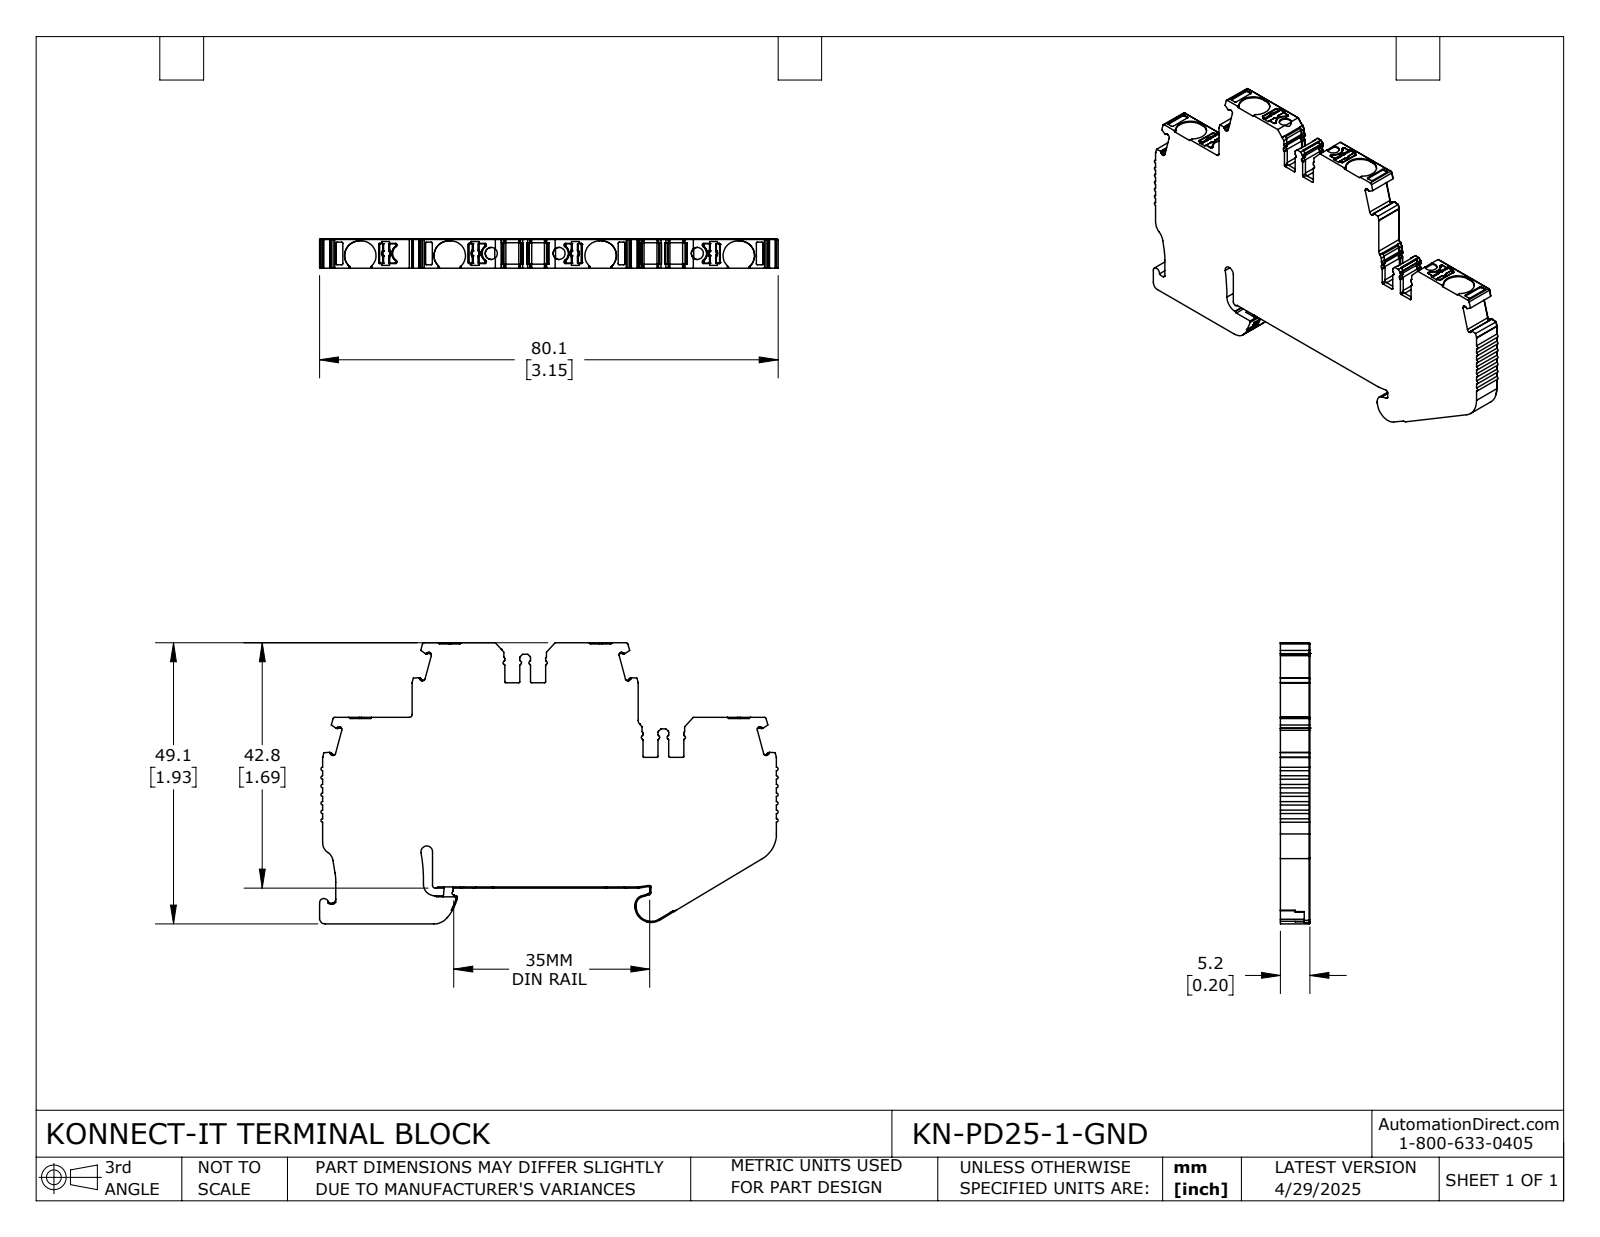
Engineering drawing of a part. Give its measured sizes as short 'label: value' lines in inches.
name: KN-PD25-1-GND
written by: SolidWorks 2024 (CONFIG_CONTROL_DESIGN)
unit: in
bodies: 1 solid, 1035 faces (503 planar, 463 cylindrical, 69 other)
size: 3.153 × 1.933 × 0.203
volume: 0.886 in³; area: 11.71 in²
holes: 3× ⌀0.083
rounds: 99× R0.008, 59× R0.012, 41× R0.004, 25× R0.016, 20× R0.02, 16× R0.006, 9× R0.024, 9× R0.039
face distances: 0.203, 0.512, 1.166, 1.678, 0.246, 1.924, 0.95, 1.412, 0.504, 0.254
hole spacings: 0.466, 0.95, 1.417
